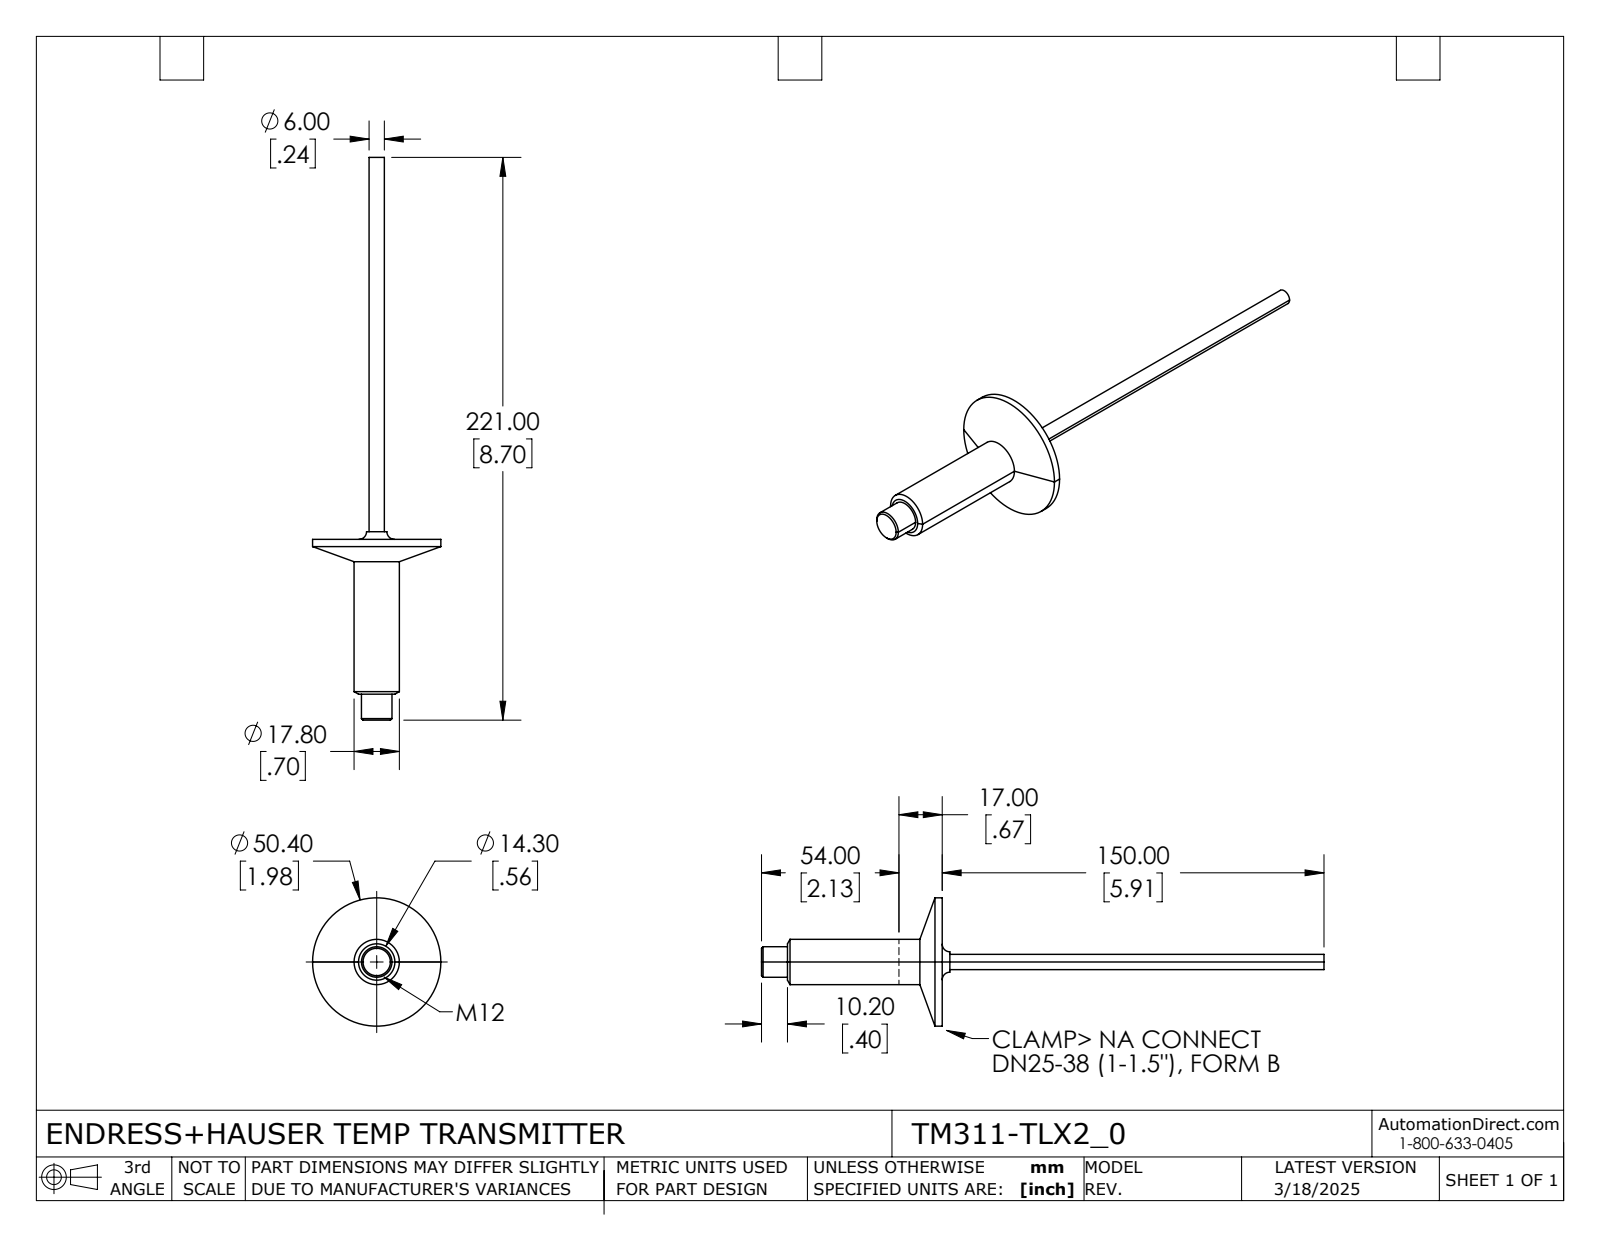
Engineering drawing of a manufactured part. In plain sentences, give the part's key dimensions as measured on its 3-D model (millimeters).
The part is named "TM311-TLX2_0". Its 3-D file was written by "SolidWorks 2021 (AUTOMOTIVE_DESIGN)". It is 1 solid with 29 faces: 6 planar, 8 cylindrical and 15 other. Overall it measures 221 by 50.4 by 50.4 millimeters. Its volume is 29 460 cubic millimeters and its surface area 10 850 square millimeters. Round bosses or shafts: 1 of diameter 50.4, 1 of diameter 17.8, 1 of diameter 12, 1 of diameter 6. The main face-to-face distances are 71, 60.8, 10.2, 150, 210.8, 221, 147, 3, 63.8, 74.
